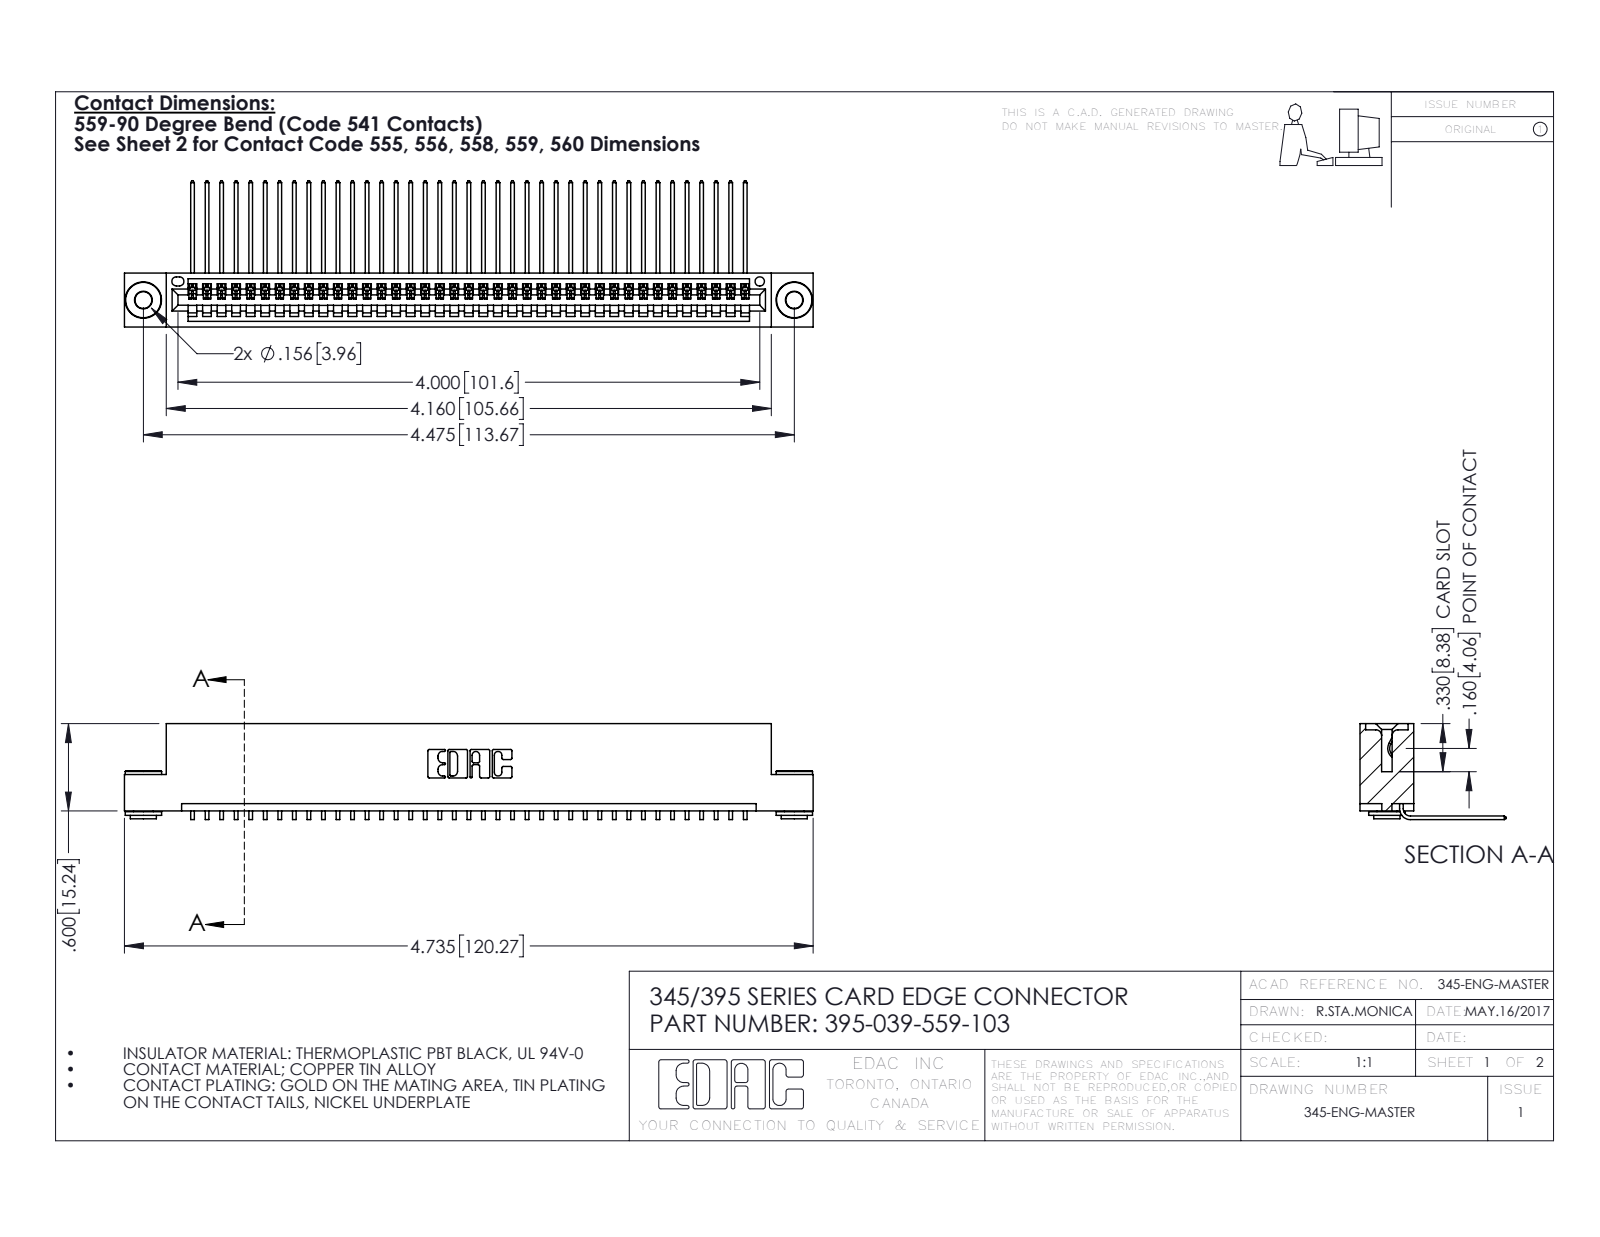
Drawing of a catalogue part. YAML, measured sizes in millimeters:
part_name: "395-039-559-103; 345-292-001_558 559 Tail - 1; 345-250-002_345-250-002-102; 345 Part_Flush Mounting Lugs - 0.156 Dia-TH"
step_written_by: "SolidWorks 2016 (CONFIG_CONTROL_DESIGN)"
units: millimeters
bodies: {solids: 42, faces: 2504, planar: 1728, cylindrical: 768, other: 8}
overall_size: [120.3, 25.5, 16.7]
volume: 11600
surface_area: 16280
round_holes:
  - {diameter: 2.9, count: 2}
  - {diameter: 4, count: 2}
  - {diameter: 1.6, count: 1}
round_bosses_or_shafts:
  - {diameter: 6.4, count: 2}
  - {diameter: 4.6, count: 2}
  - {diameter: 3.5, count: 2}
partial_cylinders:
  - {radius: 0.2, count: 78}
  - {radius: 0.3, count: 22}
  - {radius: 0.2, count: 6}
  - {radius: 0.8, count: 6}
  - {radius: 0.7, count: 3}
  - {radius: 0.8, count: 2}
  - {radius: 1, count: 2}
  - {radius: 0.4, count: 1}
face_to_face_distances: [1.8, 7.6, 9.4, 5.1, 0.6, 2.5, 6.9, 5.7, 3.8, 1.8]
hole_center_spacings: [6.9, 107.7, 113.7]
